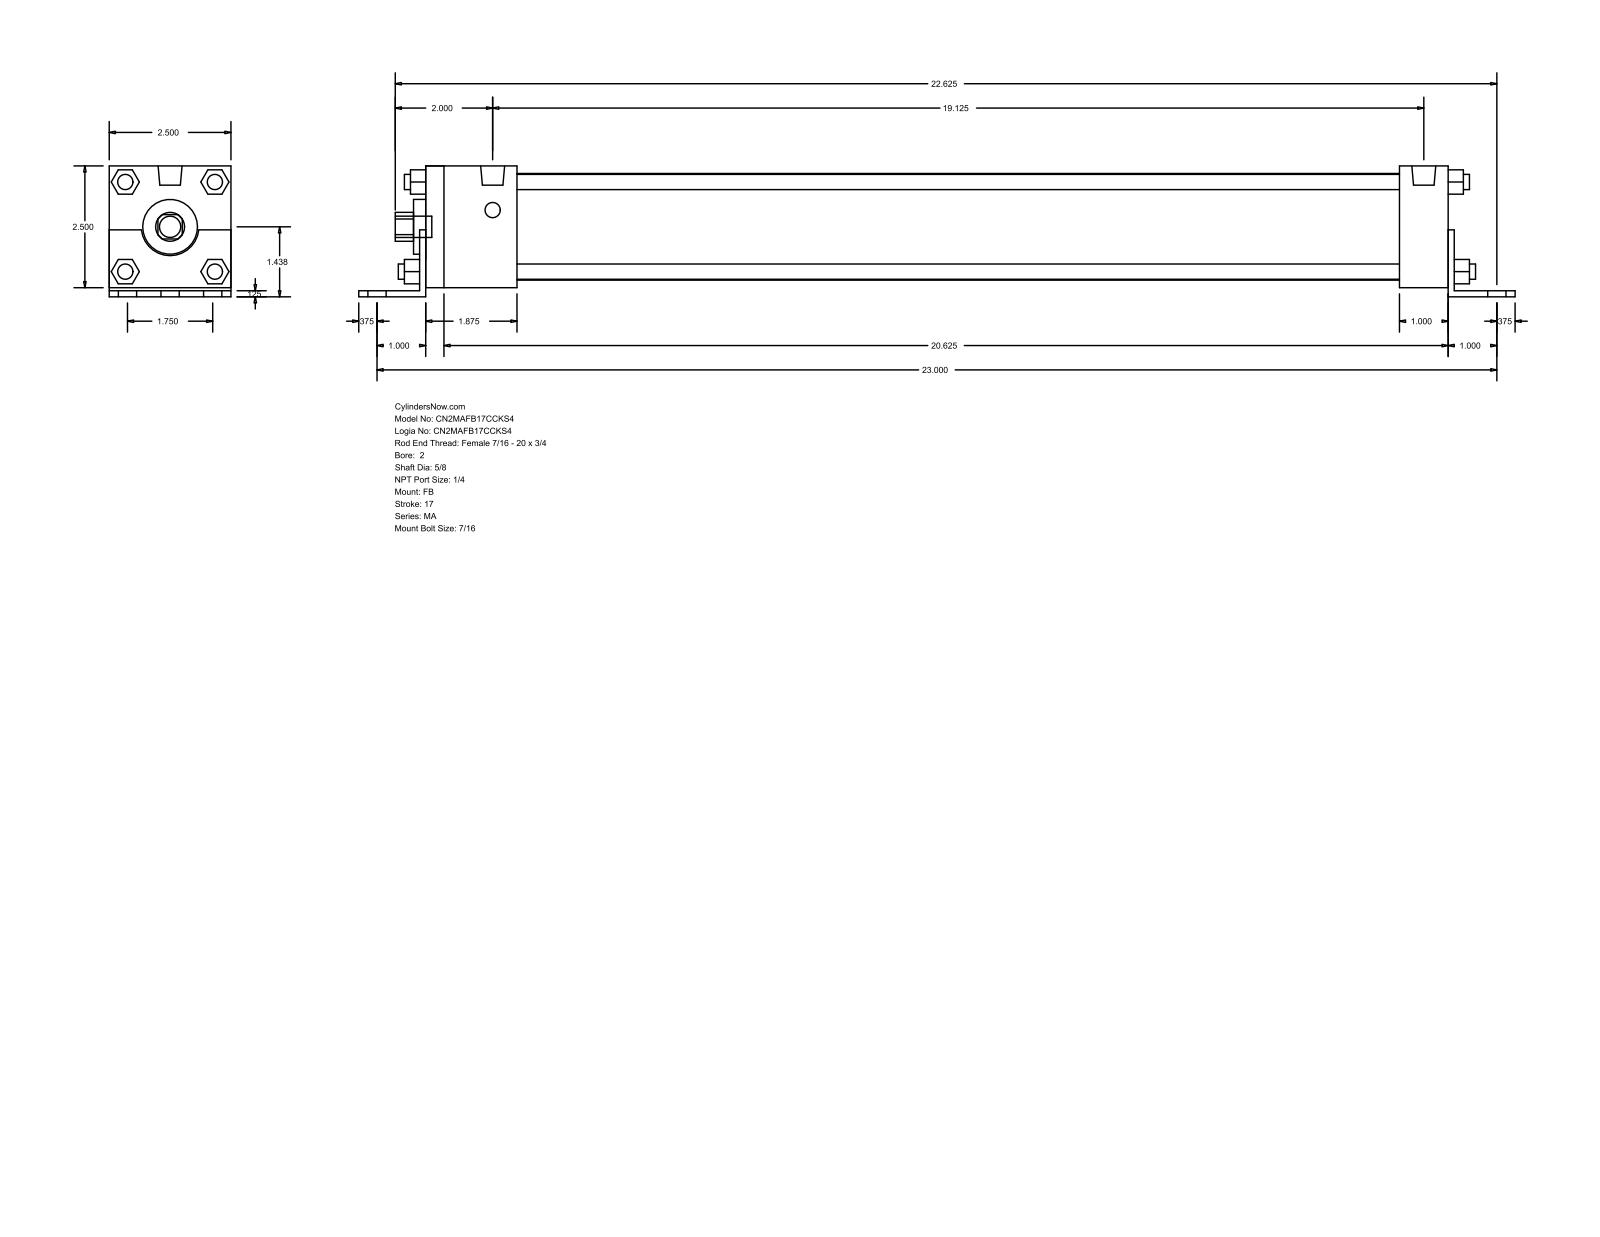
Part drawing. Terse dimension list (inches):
name: MA_FB__0200_0.625
written by: GSSL Pune (CONFIG_CONTROL_DESIGN)
unit: in
bodies: 0 solids, 140 faces (105 planar, 35 cylindrical, 0 other)
size: 23.75 × 2.687 × 2.5
holes: 1× ⌀0.625, 1× ⌀1.125, 1× ⌀2.19
bosses: 8× ⌀0.313, 7× ⌀0.437, 2× ⌀0.492
rounds: 1× R0.297, 1× R0.593
face distances: 2.5, 0.187, 0.125, 2.687, 0.063, 0.125, 2.563, 21.125, 21, 0.5
